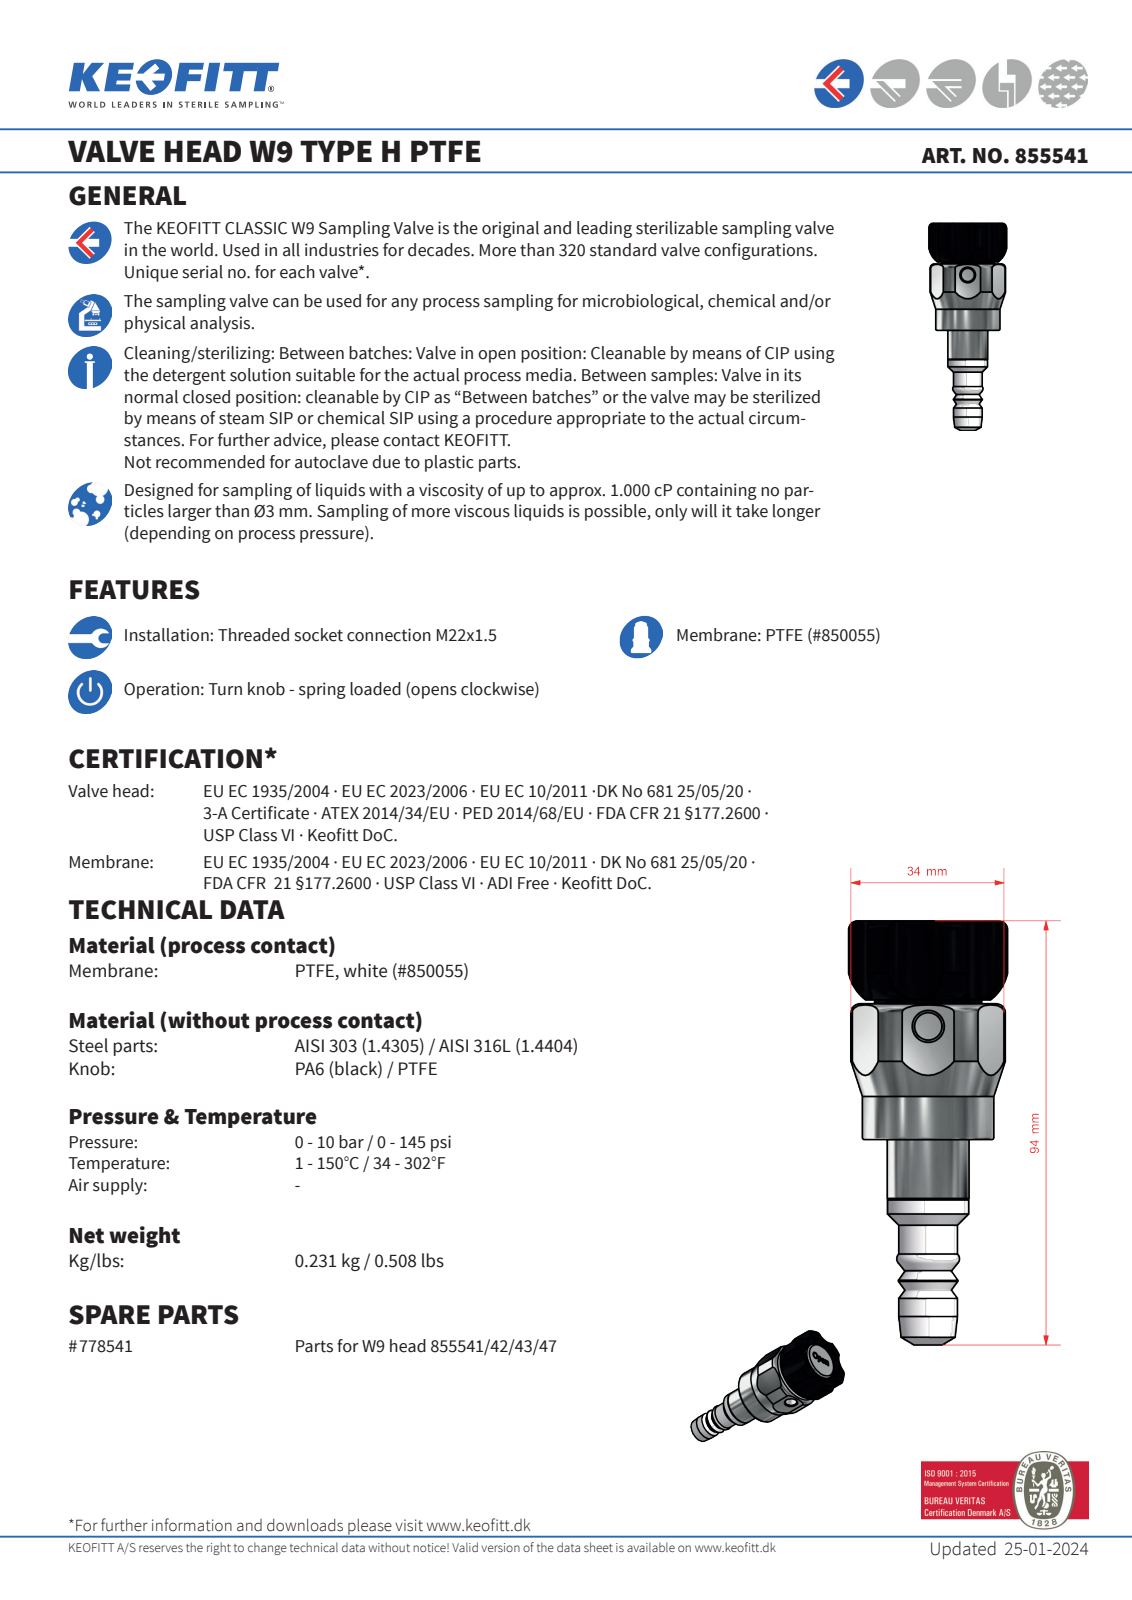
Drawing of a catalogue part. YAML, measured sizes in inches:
step_written_by: "Autodesk Inventor 2008 (AUTOMOTIVE_DESIGN)"
units: inches
bodies: {solids: 1, faces: 152, planar: 54, cylindrical: 33, other: 65}
overall_size: [3.642, 1.378, 1.357]
volume: 2.655
surface_area: 13.73
round_holes:
  - {diameter: 0.12, count: 1}
  - {diameter: 0.238, count: 1}
  - {diameter: 0.921, count: 1}
round_bosses_or_shafts:
  - {diameter: 0.118, count: 3}
  - {diameter: 1.142, count: 1}
  - {diameter: 0.709, count: 1}
  - {diameter: 0.705, count: 1}
  - {diameter: 0.682, count: 1}
  - {diameter: 0.512, count: 1}
partial_cylinders:
  - {radius: 0.315, count: 6}
  - {radius: 0.669, count: 1}
  - {radius: 0.689, count: 1}
face_to_face_distances: [1.26, 1.841, 1.86, 0.02, 1.831, 1.851, 1.181, 1.172, 0.659, 0.679]
hole_center_spacings: [0.079]
